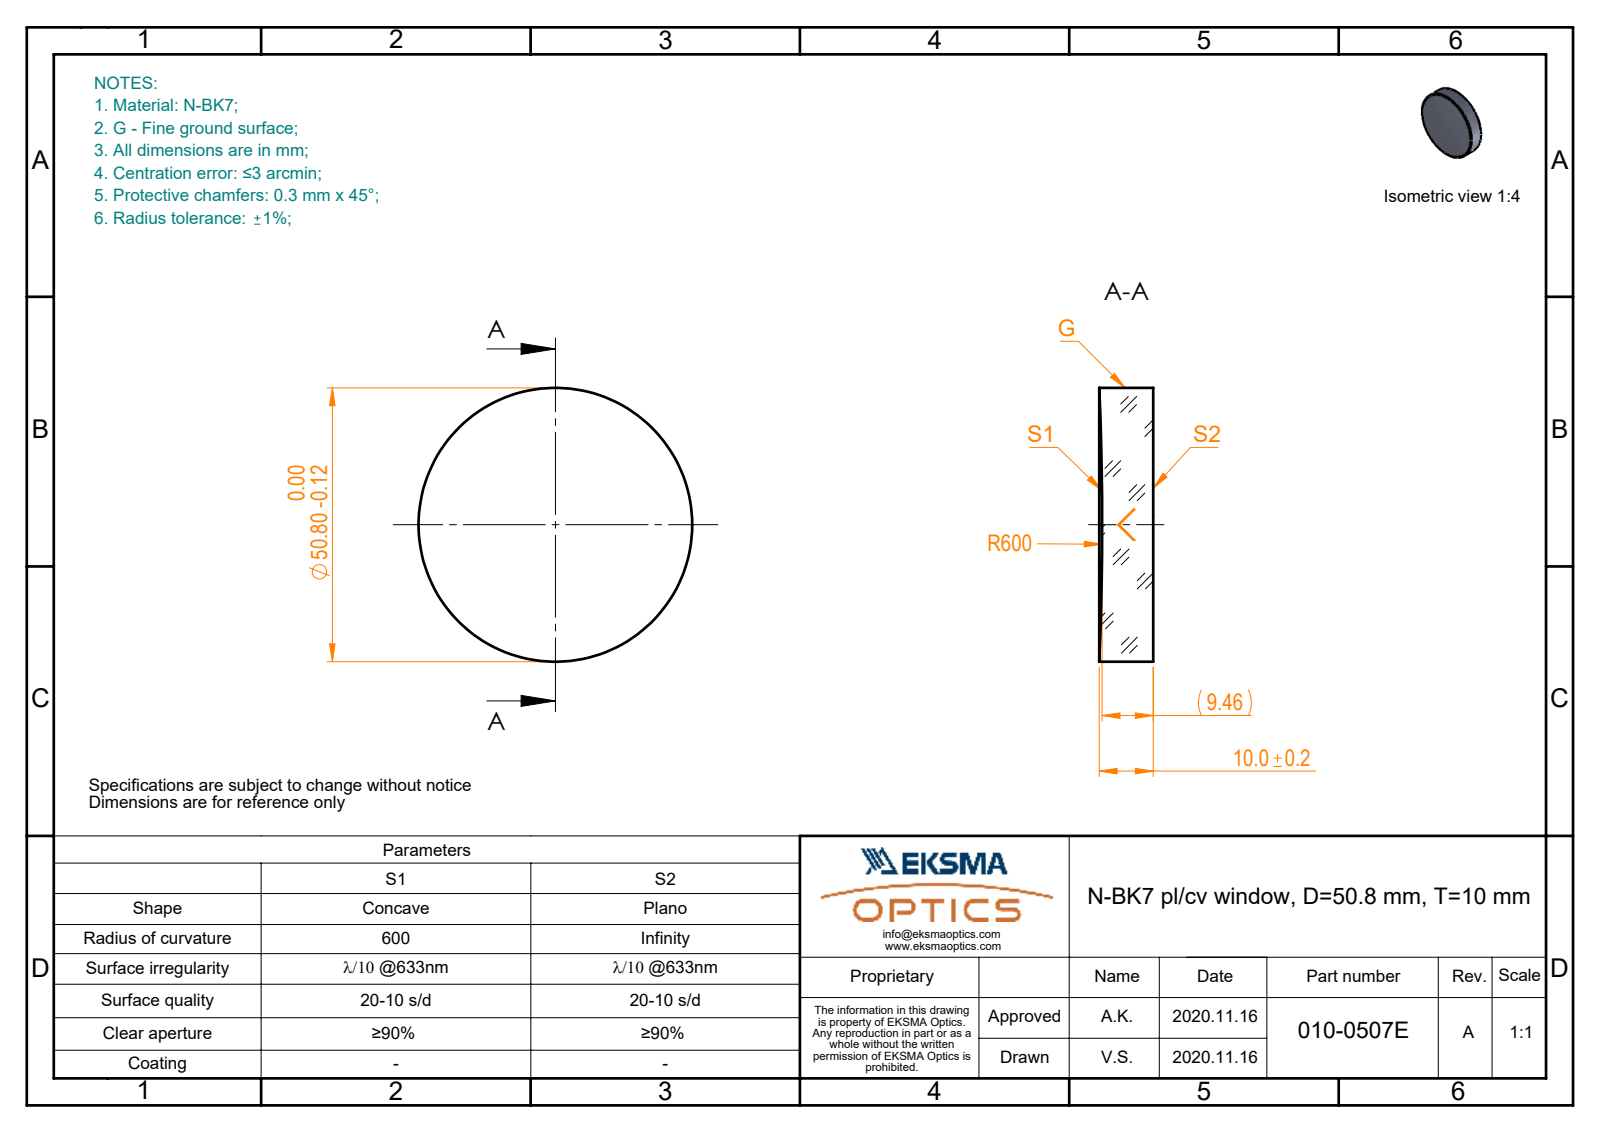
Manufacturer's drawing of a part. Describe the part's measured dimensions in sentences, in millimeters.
The part is named "010-0507E_N-BK7_PCV_window". Its 3-D file was written by "SolidWorks 2019 (CONFIG_CONTROL_DESIGN)". It is 1 solid with 5 faces: 1 planar, 2 cylindrical and 2 other. Overall it measures 50.8 by 50.8 by 10 millimeters. Its volume is 19 723 cubic millimeters and its surface area 5 650 square millimeters. Round bosses or shafts: 1 of diameter 50.8.
